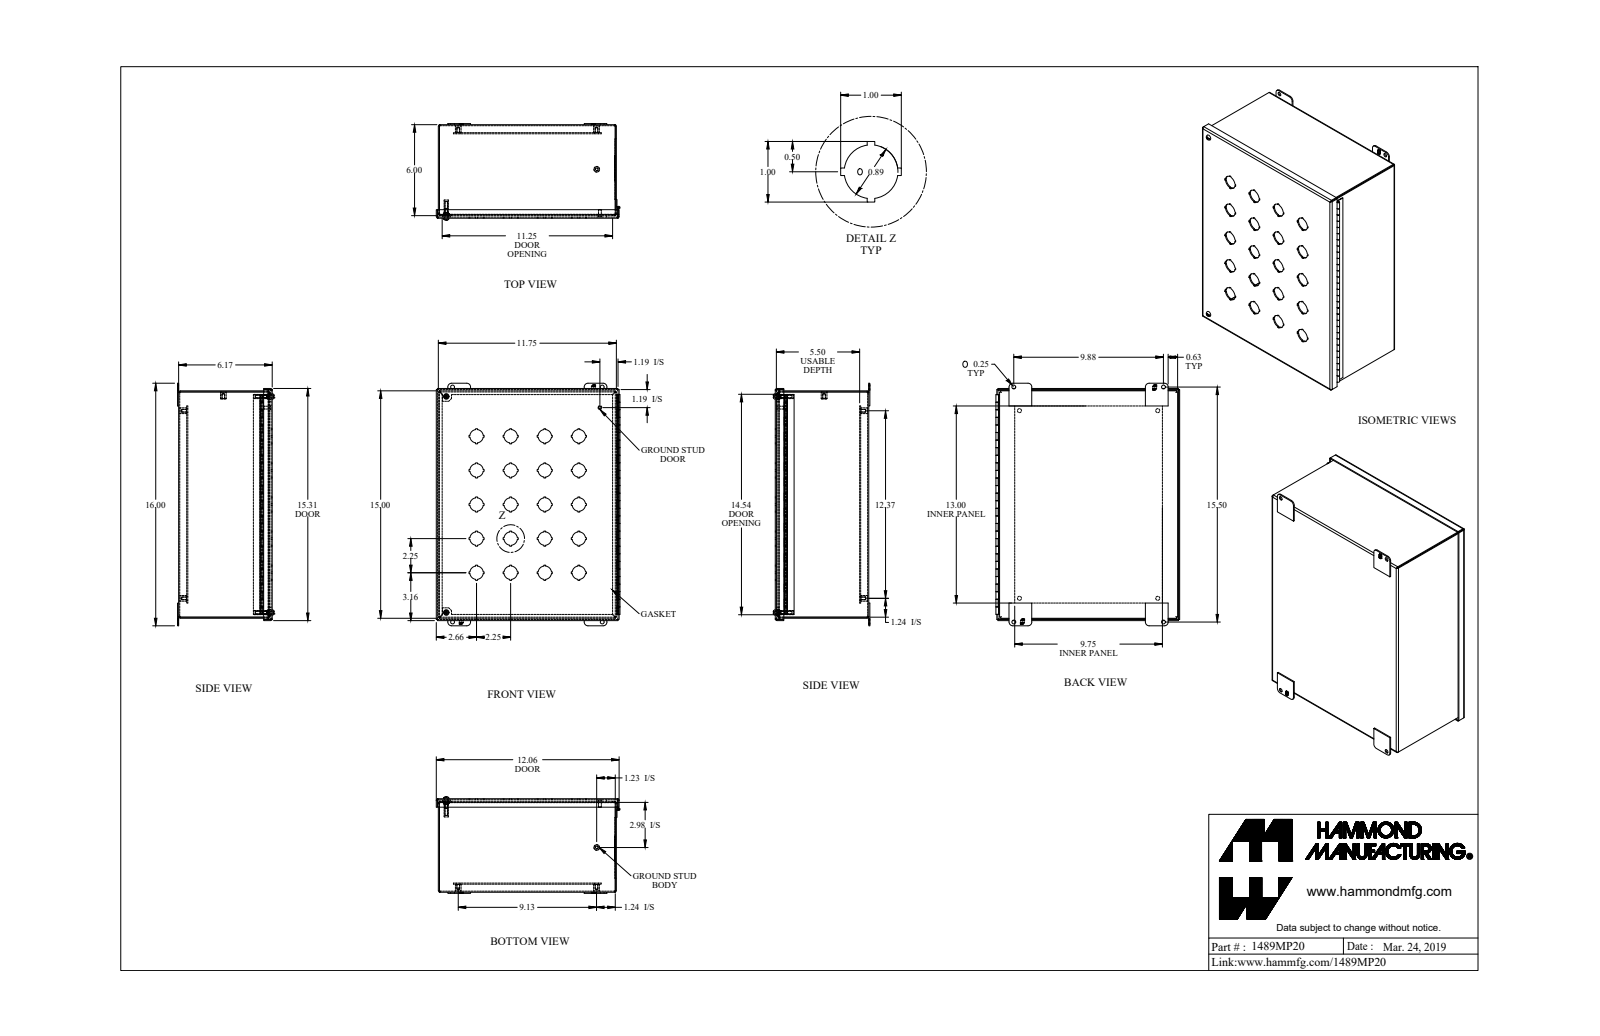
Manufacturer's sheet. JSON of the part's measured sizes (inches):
{"part_name": "1489MP20_Default", "step_written_by": "SolidWorks 2019 (CONFIG_CONTROL_DESIGN)", "units": "inches", "bodies": {"solids": 21, "faces": 1087, "planar": 754, "cylindrical": 275, "other": 58}, "overall_size": [16, 12.123, 6.371], "volume_in3": 68.02, "surface_area_in2": 1826, "round_holes": [[0.886, 20], [0.25, 6], [0.156, 5], [0.265, 4], [0.159, 2], [0.406, 2]], "round_bosses_or_shafts": [[0.375, 5], [0.39, 2], [0.275, 2], [0.19, 2], [0.148, 2], [0.25, 1], [0.188, 1], [0.174, 1]], "partial_cylinders_radius": [[0.036, 12], [0.108, 12], [0.25, 8], [0.16, 2], [0.171, 2], [0.125, 1]], "face_to_face_distances": [0.072, 6.1, 5.568, 0.532, 6.172, 11.678, 0.072, 6.028, 0.604, 14.928], "hole_center_spacings": [5.031, 2.25, 3.182, 4.5, 7.115, 8.113, 6.75, 6.364]}
